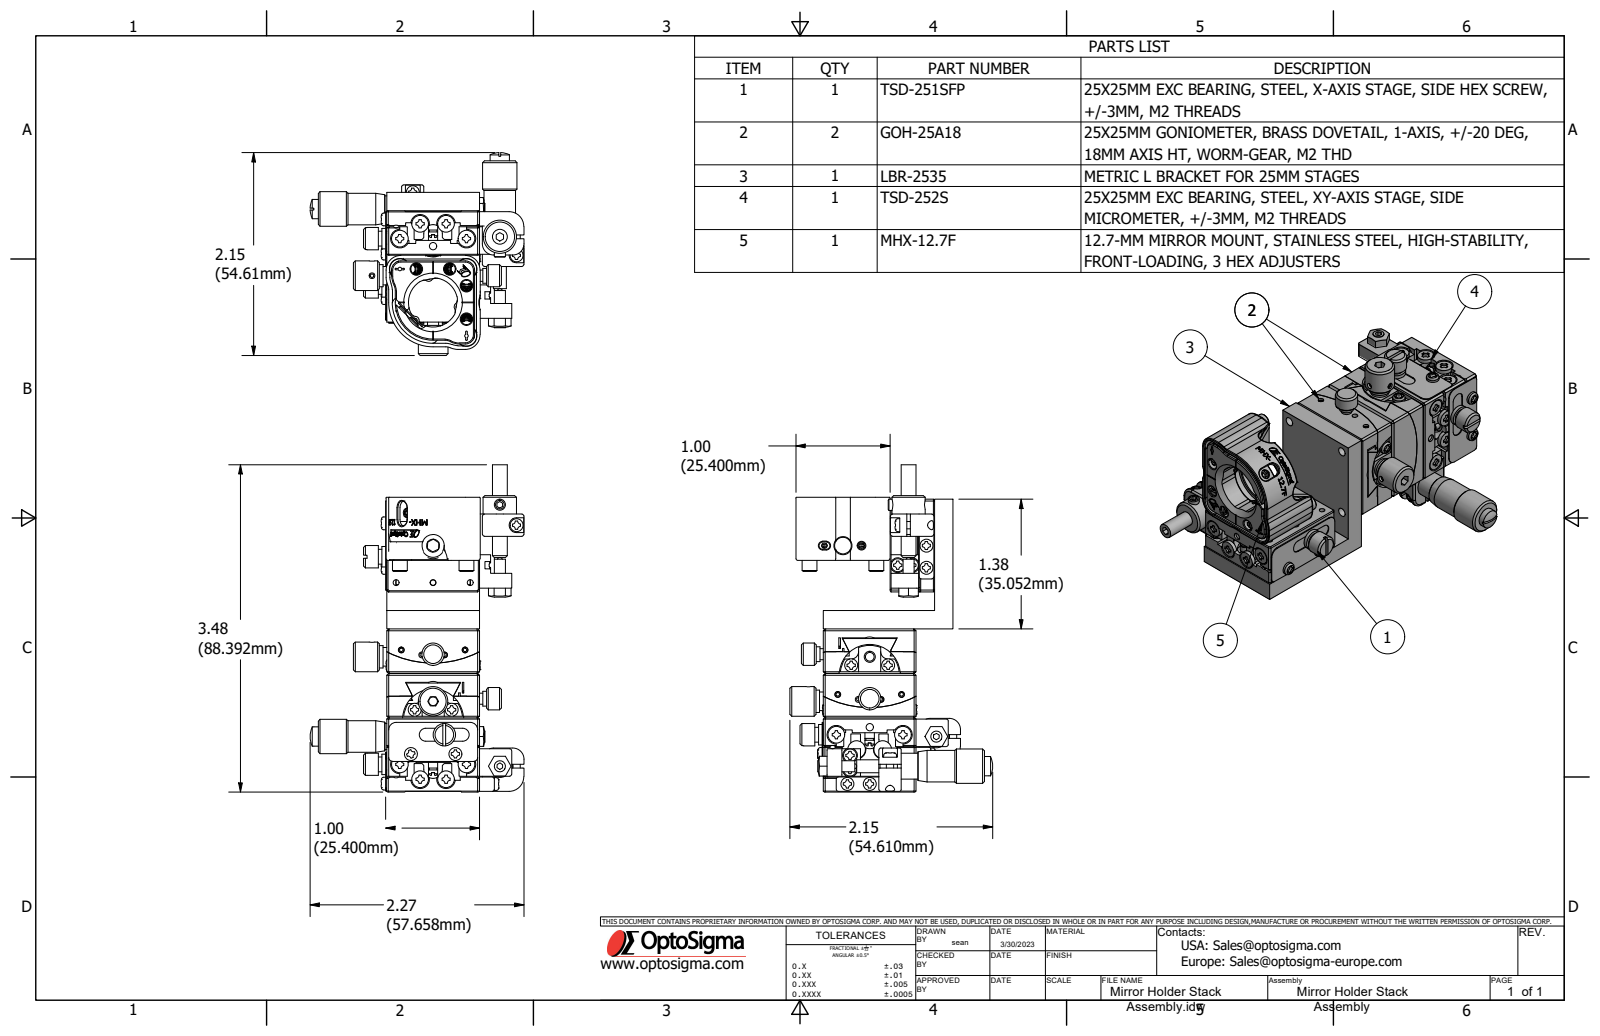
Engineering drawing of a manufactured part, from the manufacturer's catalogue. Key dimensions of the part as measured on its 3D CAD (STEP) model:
Part name (STEP PRODUCT): Mirror Holder Stack Assembly; TSD-251SFP; TSD-251SFP-C1-S07; TSD-251SFP-C1-S08 (+5 more)
STEP written by: Autodesk Inventor 2022 (AUTOMOTIVE_DESIGN)
Units: millimetres
Bodies: 19 solids, 3825 faces (1921 planar, 1210 cylindrical, 694 other)
Overall size (bounding box): 88.3 × 57.7 × 54.7
Volume: 49 673 mm³ · Surface area: 46 790 mm²
Round holes (diameter × count): ⌀1.57 ×42, ⌀1.57 ×42, ⌀1.8 ×35, ⌀2.2 ×22, ⌀2.4 ×17, ⌀2.5 ×16, ⌀4 ×14, ⌀3 ×11, ⌀2 ×9, ⌀1.5 ×7, ⌀6 ×7, ⌀1.6 ×6
Round bosses / shafts (diameter × count): ⌀2 ×49, ⌀4.5 ×16, ⌀3 ×12, ⌀1.8 ×12, ⌀4 ×10, ⌀2.5 ×8, ⌀0.4 ×8, ⌀6 ×7
Partial cylindrical surfaces — rounded edges, fillets, slot ends (radius × count): R0.8 ×156, R0.5 ×67, R0.2 ×54, R1 ×24, R2 ×19, R2.5 ×19, R3 ×14, R0.15 ×12
Main face-to-face distances: 12, 5, 25, 4, 17, 8, 7.7, 24, 10, 3.7
Hole centre spacings: 10, 22.36, 6, 20, 12, 14.14, 13.79, 18.12
